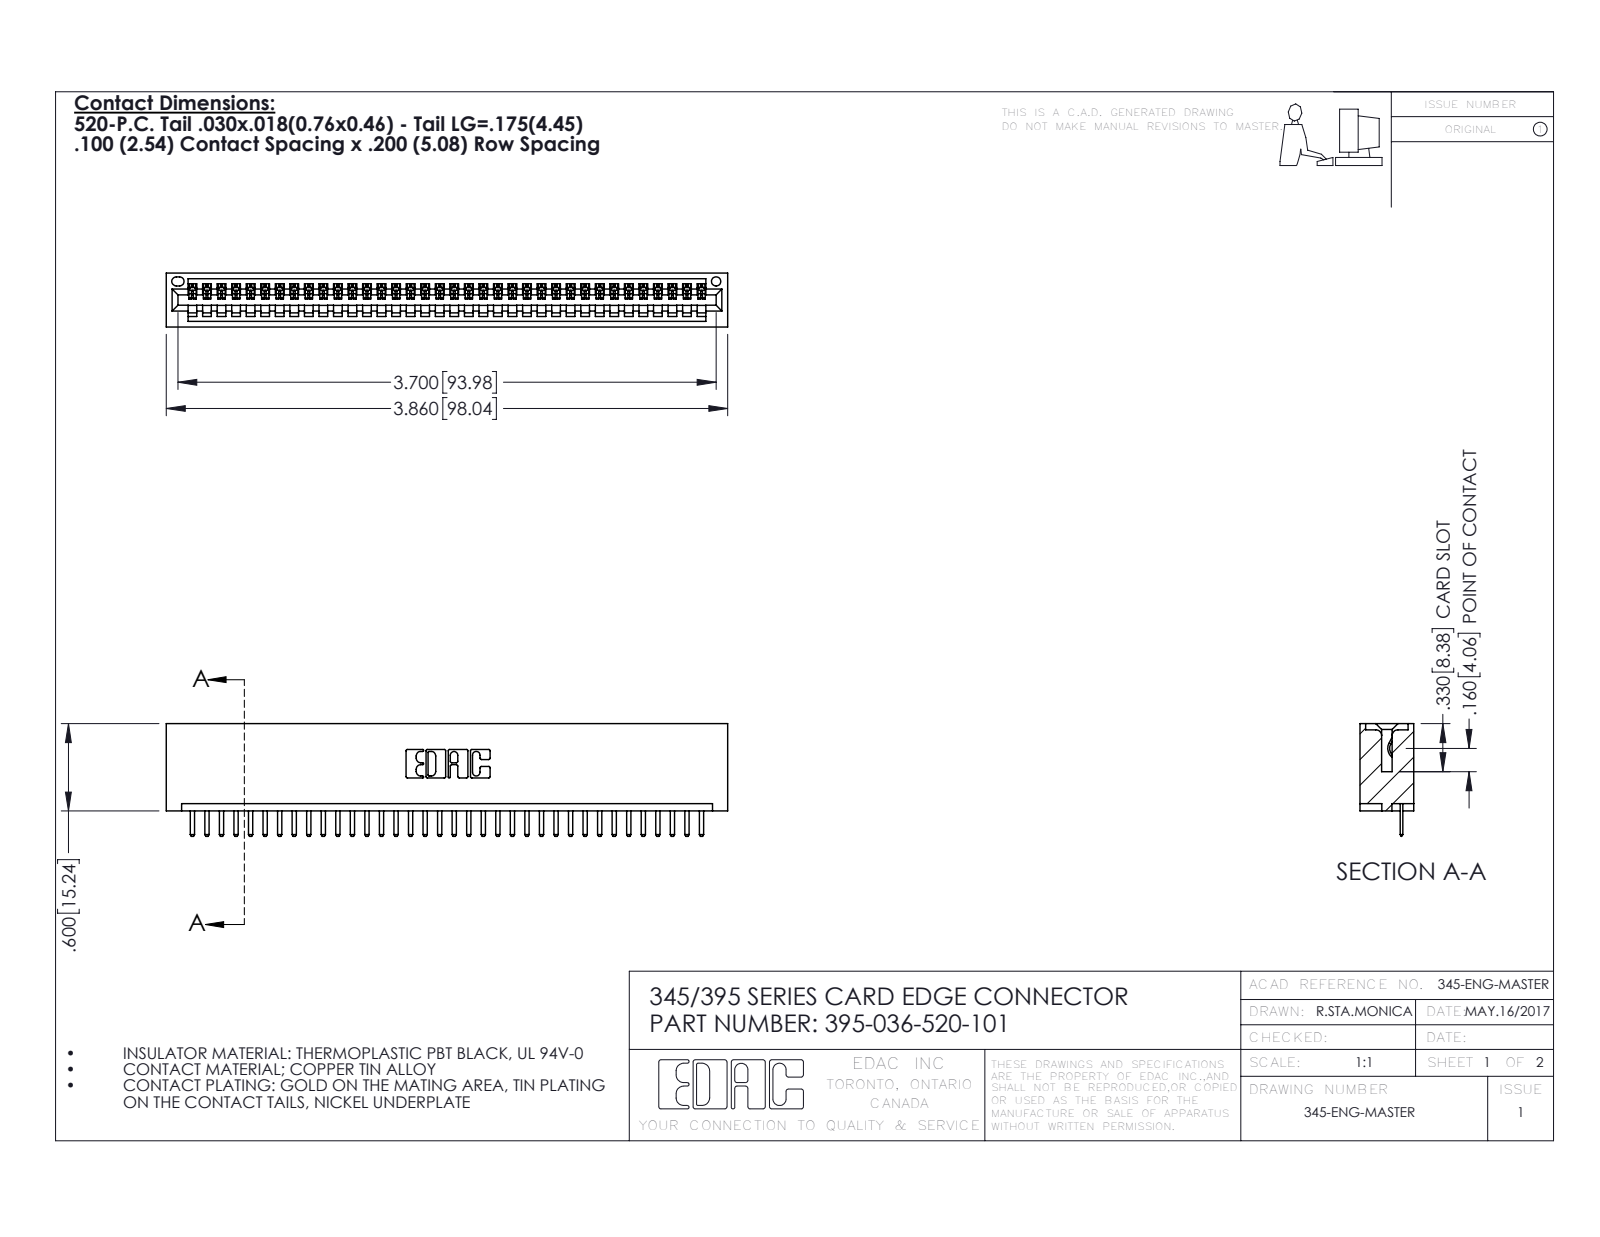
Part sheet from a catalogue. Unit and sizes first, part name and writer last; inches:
Units: inches
Overall size (bounding box): 3.86 × 0.775 × 0.37
Round holes (diameter × count): ⌀0.064 ×1
Partial cylindrical surfaces — rounded edges, fillets, slot ends (radius × count): R0.01 ×74, R0.006 ×72, R0.01 ×22, R0.007 ×6, R0.031 ×6, R0.026 ×3, R0.031 ×2, R0.04 ×2
Main face-to-face distances: 0.298, 0.072, 0.37, 0.2, 0.098, 0.272, 0.025, 0.225, 0.072, 0.149
Volume: 0.595 in³ · Surface area: 19.71 in²
Bodies: 37 solids, 2350 faces (1588 planar, 762 cylindrical, 0 other)
Part name (STEP PRODUCT): 395-036-520-101; 345 Part_No Mounting Lugs; 345-292-001_345-293-120
STEP written by: SolidWorks 2016 (CONFIG_CONTROL_DESIGN)
